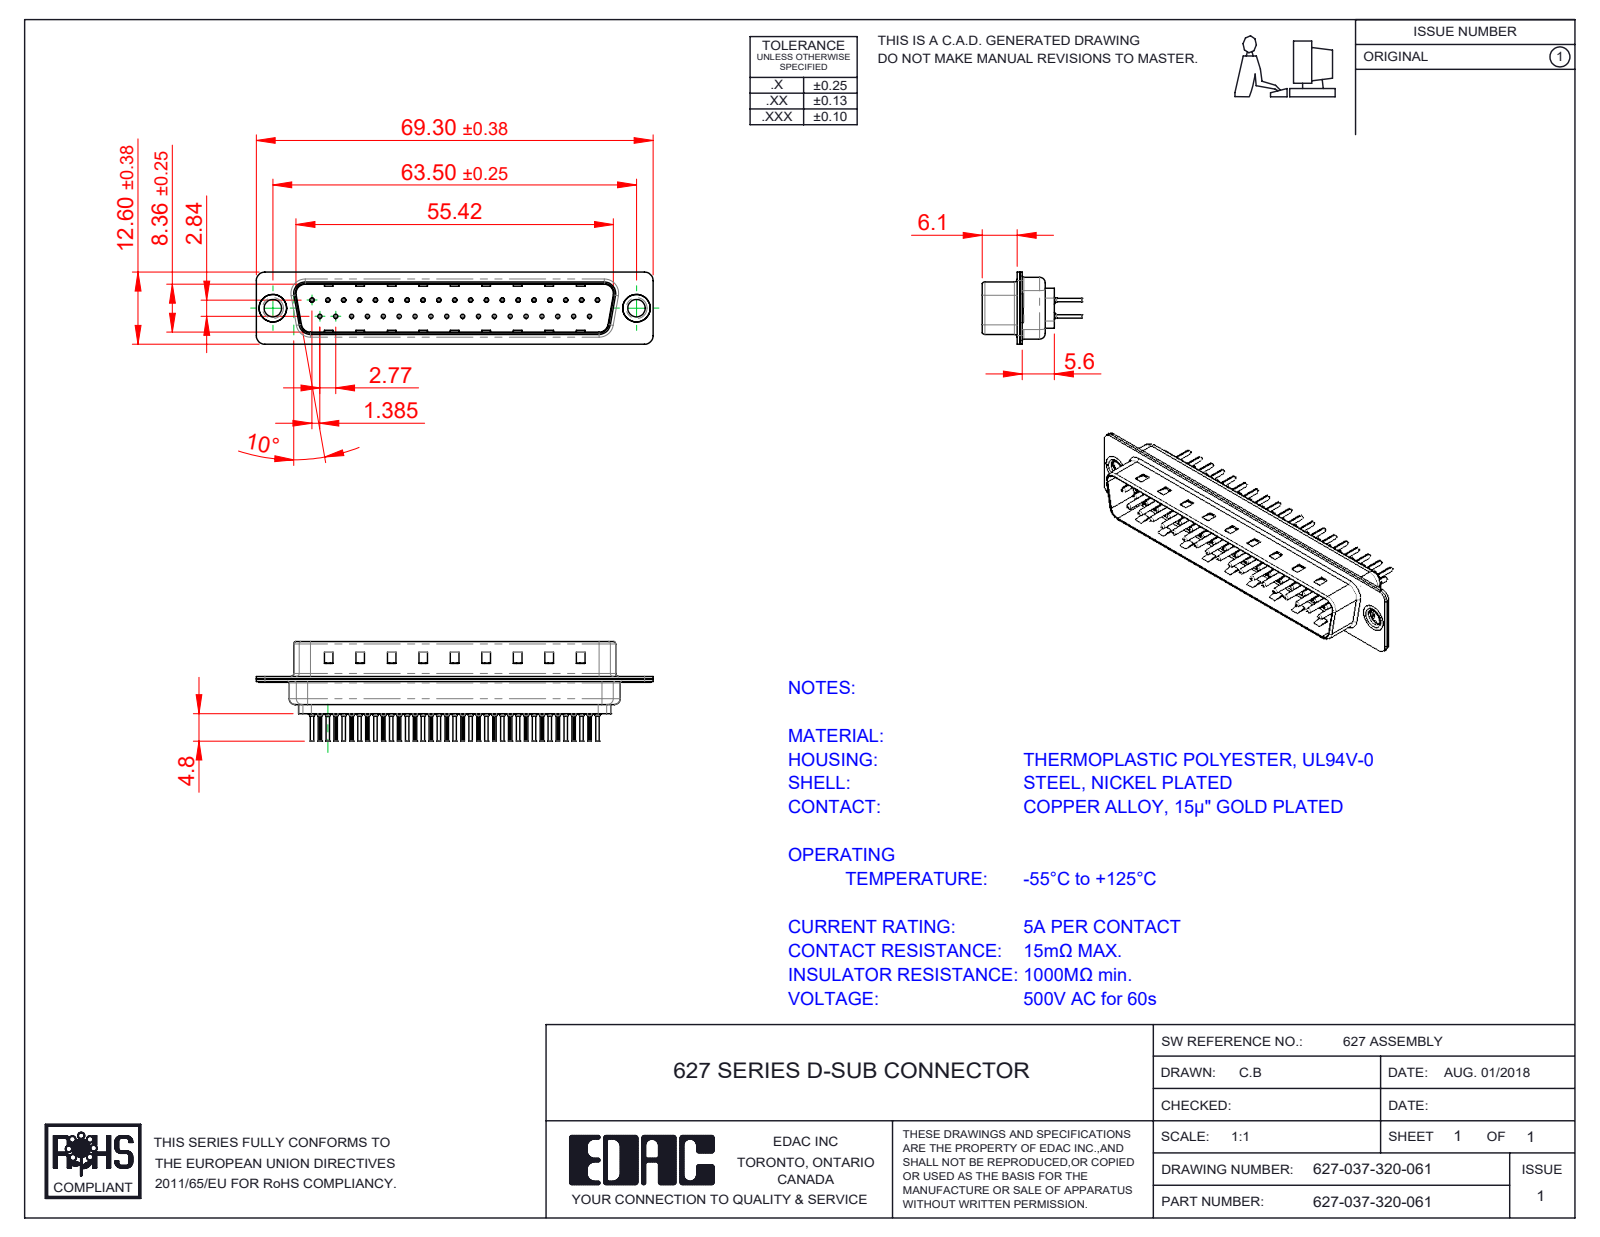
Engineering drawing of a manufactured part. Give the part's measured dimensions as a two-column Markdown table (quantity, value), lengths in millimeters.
| quantity | value |
| --- | --- |
| part name | 627 Thru Hole Rivet; 627 Shell Rear_37 Contacts; 627 Contact Row 2_20L; 627 Contact Row 1_20L (+3 more) |
| STEP written by | SolidWorks 2020 (CONFIG_CONTROL_DESIGN) |
| units | millimeters |
| bodies | 42 solids, 4012 faces (1091 planar, 1494 cylindrical, 1427 other) |
| overall size | 69.3 × 17.3 × 12.6 |
| volume | 3 624 mm³ |
| surface area | 10 536 mm² |
| round holes (diameter × count) | 0.2 × 37, 0.35 × 37, 1.1 × 37, 1.6 × 37, 3.05 × 2, 4 × 2, 4.8 × 2 |
| round bosses / shafts (diameter × count) | 2 × 37, 1.5 × 37, 0.75 × 37, 0.6 × 37, 5 × 2, 4.9 × 2, 3.55 × 2 |
| partial cylindrical surfaces (radius × count) | 0.1 × 74, 1.5 × 16, 2 × 12, 0.5 × 8, 1.6 × 8, 0.25 × 4, 0.6 × 4, 0.65 × 4 |
| main face-to-face distances | 0.4, 0.82, 9.58, 0.45, 8.76, 1.5, 0.9, 1.4, 6.05, 0.5 |
| hole center spacings | 3.16, 2.77, 5.54, 8.31, 5.04, 10.1, 11.08, 12.78 |
